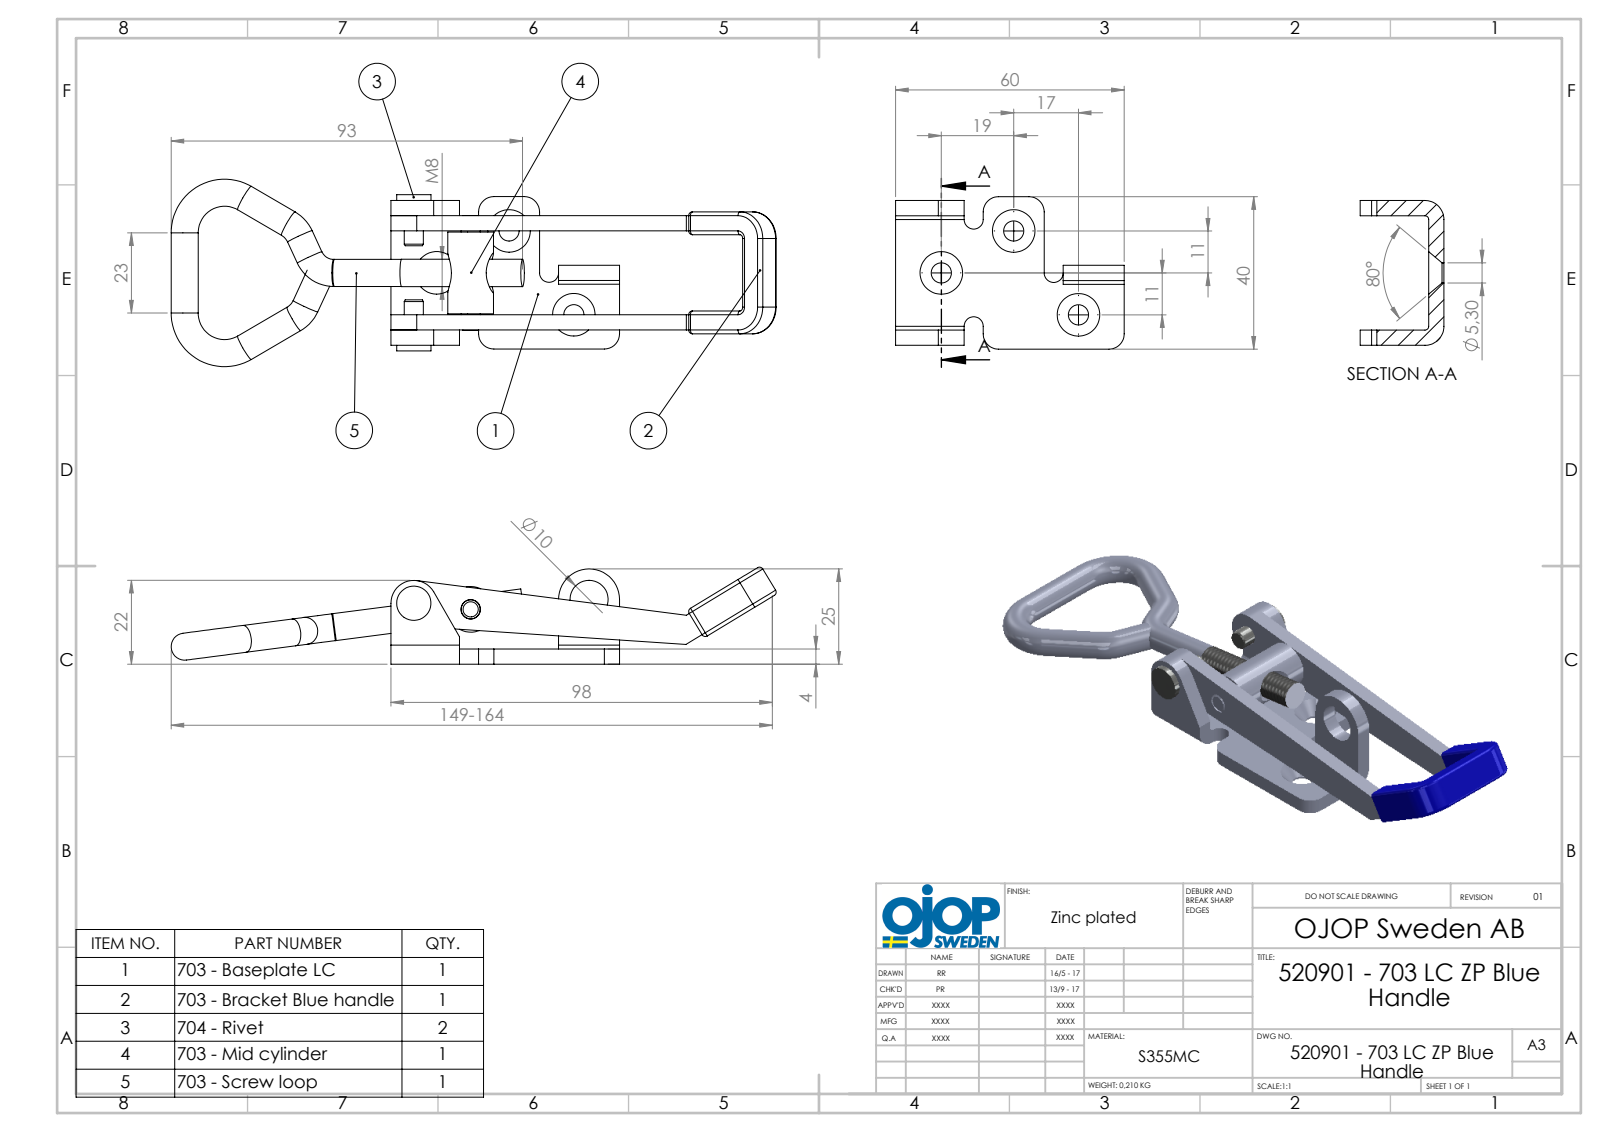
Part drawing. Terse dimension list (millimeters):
name: 703 - Rulle; 703 - Skruvögla; 520901 - 703 LC ZP Blue; 703- Platta LC (+2 more)
written by: SolidWorks 2015 (AUTOMOTIVE_DESIGN)
unit: mm
bodies: 6 solids, 213 faces (66 planar, 93 cylindrical, 54 other)
size: 161.29 × 49.4 × 25.47
volume: 28 204 mm³; area: 18 843 mm²
holes: 3× ⌀5.3, 2× ⌀5.1, 1× ⌀7.2, 1× ⌀7.7, 1× ⌀10
bosses: 4× ⌀7, 2× ⌀5, 1× ⌀12, 1× ⌀9, 1× ⌀7.7
rounds: 23× R1, 4× R4, 3× R2.5, 3× R5, 2× R7, 1× R6, 1× R8
face distances: 4, 26, 30, 22, 17, 13, 9, 21, 8, 5
hole spacings: 15.01, 21.95, 27.8, 31.19, 37.64, 46.01
